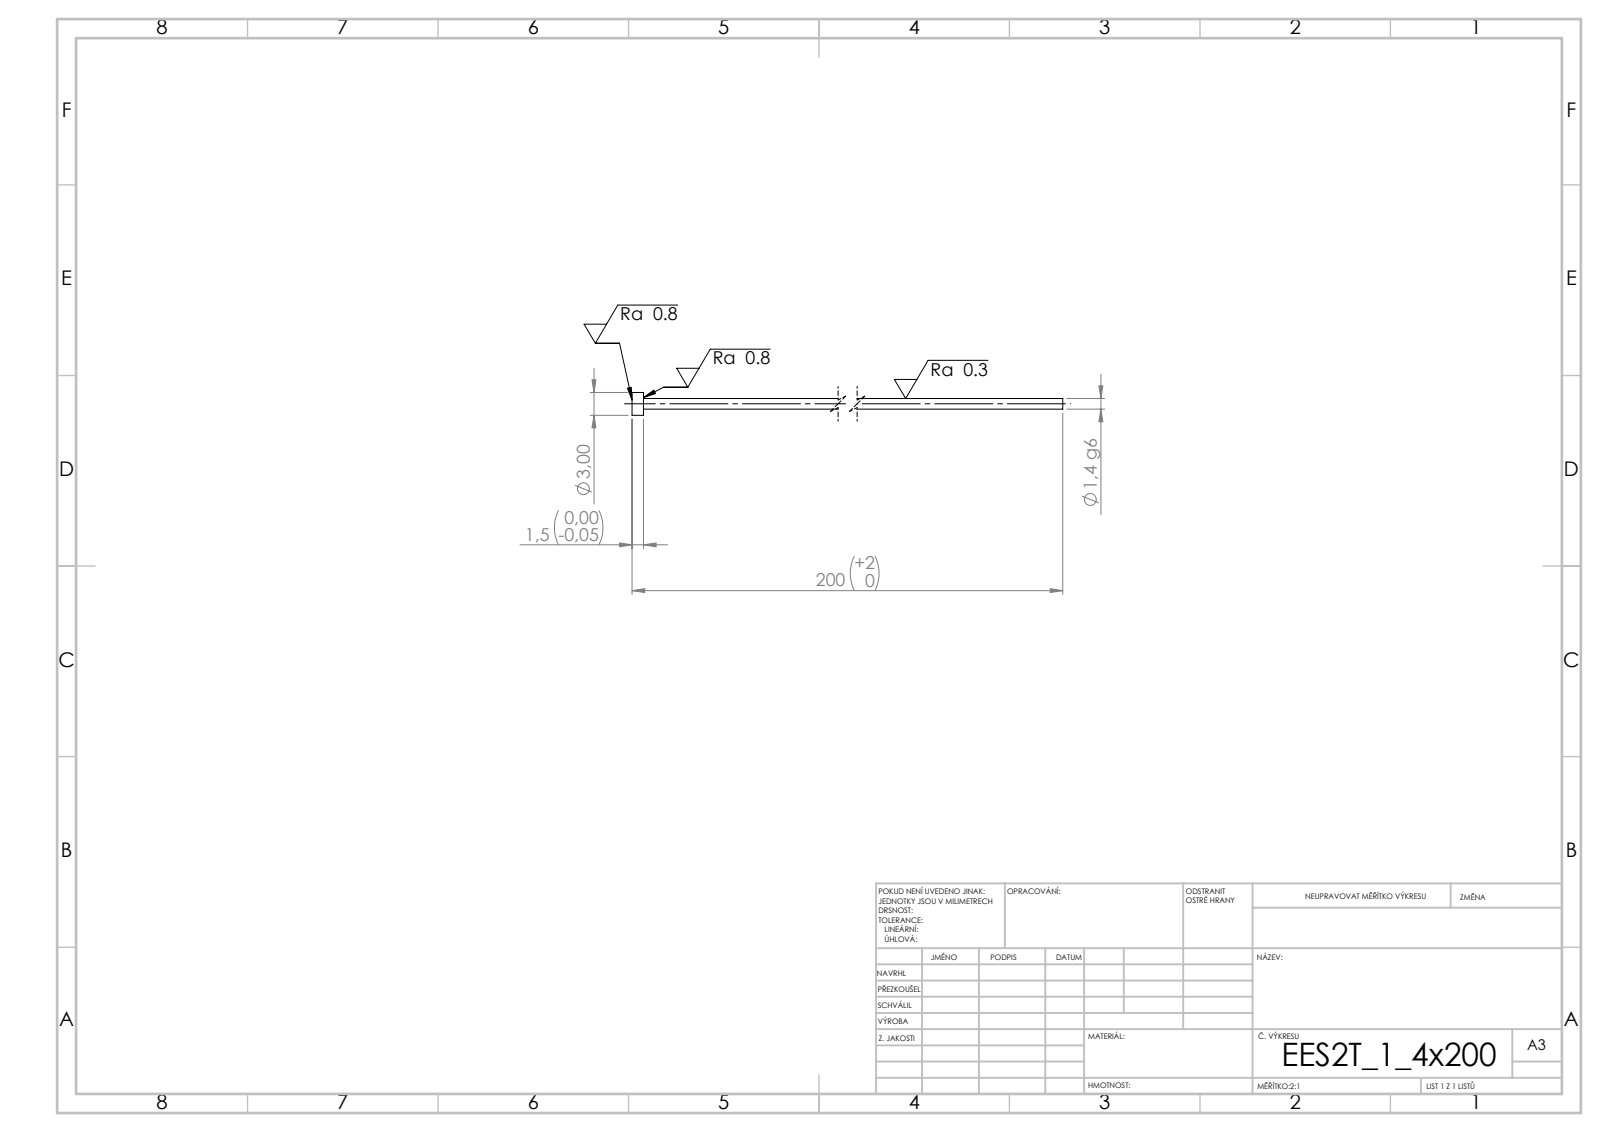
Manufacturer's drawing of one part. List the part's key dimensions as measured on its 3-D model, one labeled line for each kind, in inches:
STEP written by: SolidWorks 2019 (CONFIG_CONTROL_DESIGN)
Units: inches
Bodies: 1 solid, 7 faces (3 planar, 4 cylindrical, 0 other)
Overall size (bounding box): 7.874 × 0.118 × 0.118
Volume: 0.019 in³ · Surface area: 1.4 in²
Round bosses / shafts (diameter × count): ⌀0.118 ×1, ⌀0.055 ×1
Main face-to-face distances: 0.059, 7.874, 7.815
